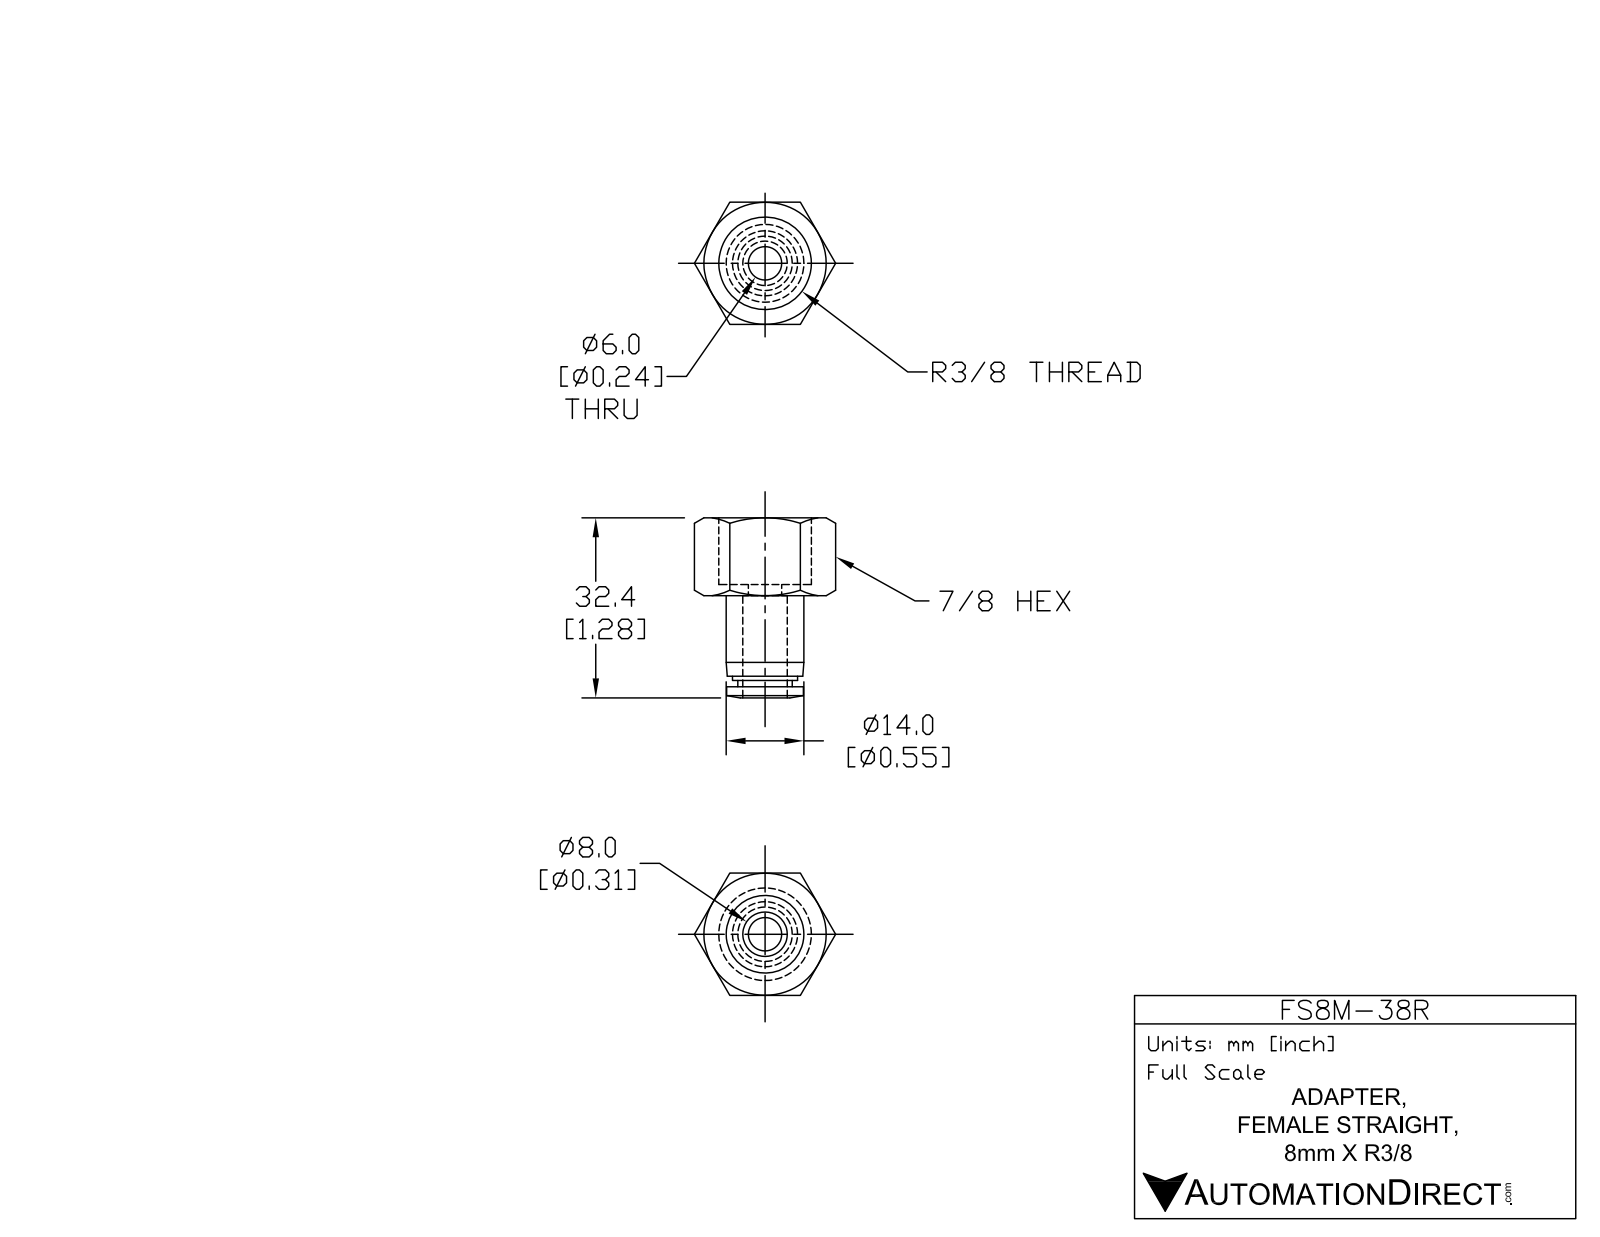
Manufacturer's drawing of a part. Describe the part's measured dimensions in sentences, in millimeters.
The part is named "FS8M-38R". Its 3-D file was written by "SolidWorks 2015 (AUTOMOTIVE_DESIGN)". It is 1 solid with 48 faces: 14 planar, 12 cylindrical and 22 other. Overall it measures 32.4 by 25.4 by 22 millimeters. Its volume is 4 970 cubic millimeters and its surface area 3 828 square millimeters. Round holes: 1 of diameter 6, 1 of diameter 8.3. Round bosses or shafts: 1 of diameter 14, 1 of diameter 13.8, 1 of diameter 11.7, 1 of diameter 9.8. The main face-to-face distances are 22, 2, 12, 14, 18.4, 30.4, 16.4, 28.5, 16.5, 14.5.
